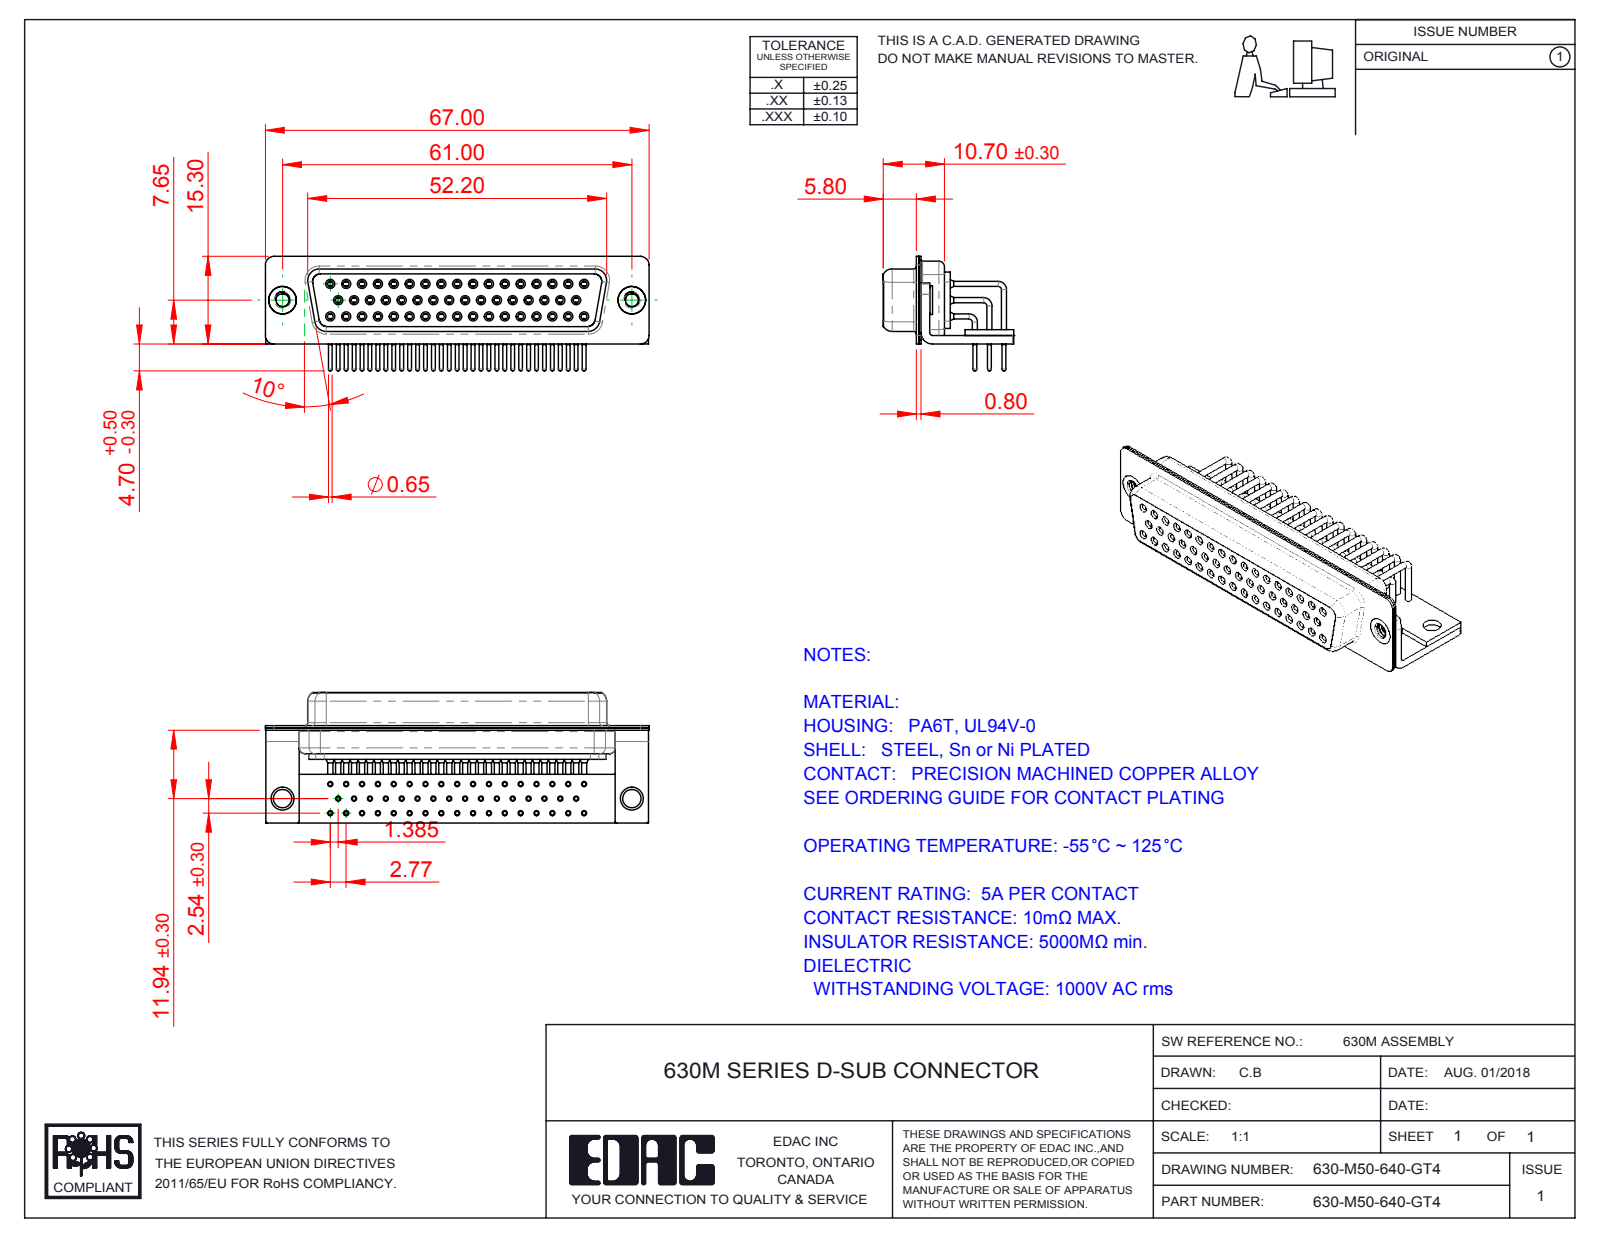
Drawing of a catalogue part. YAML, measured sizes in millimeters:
part_name: "630M Contact Row 2_50 Contacts; 630-M50-640-GT4; 630M 4-40 Threaded Rivet_Stabilizer; 630M Contact Row 1_50 Contacts (+6 more)"
step_written_by: "SolidWorks 2016 (CONFIG_CONTROL_DESIGN)"
units: millimeters
bodies: {solids: 58, faces: 3079, planar: 843, cylindrical: 1409, other: 827}
overall_size: [67, 22.8, 20]
volume: 7864
surface_area: 18601
round_holes:
  - {diameter: 0.9, count: 50}
  - {diameter: 1, count: 50}
  - {diameter: 1.1, count: 50}
  - {diameter: 1.7, count: 50}
  - {diameter: 1.8, count: 50}
  - {diameter: 2, count: 50}
  - {diameter: 2.26, count: 2}
  - {diameter: 3.2, count: 2}
  - {diameter: 4, count: 2}
  - {diameter: 4.8, count: 2}
round_bosses_or_shafts:
  - {diameter: 0.9, count: 59}
  - {diameter: 1.6, count: 50}
  - {diameter: 1.5, count: 50}
  - {diameter: 0.65, count: 50}
  - {diameter: 5, count: 2}
  - {diameter: 4.9, count: 2}
partial_cylinders:
  - {radius: 0.25, count: 16}
  - {radius: 1.5, count: 16}
  - {radius: 2, count: 13}
  - {radius: 1.35, count: 8}
  - {radius: 1.6, count: 8}
  - {radius: 0.5, count: 5}
  - {radius: 0.6, count: 4}
  - {radius: 0.65, count: 4}
face_to_face_distances: [0.4, 1, 2.2, 0.85, 1.35, 11.85, 12.25, 5.8, 5.9, 0.8]
hole_center_spacings: [2.77, 5.54, 8.31, 11.08, 13.85, 16.62, 3.16, 19.39]
